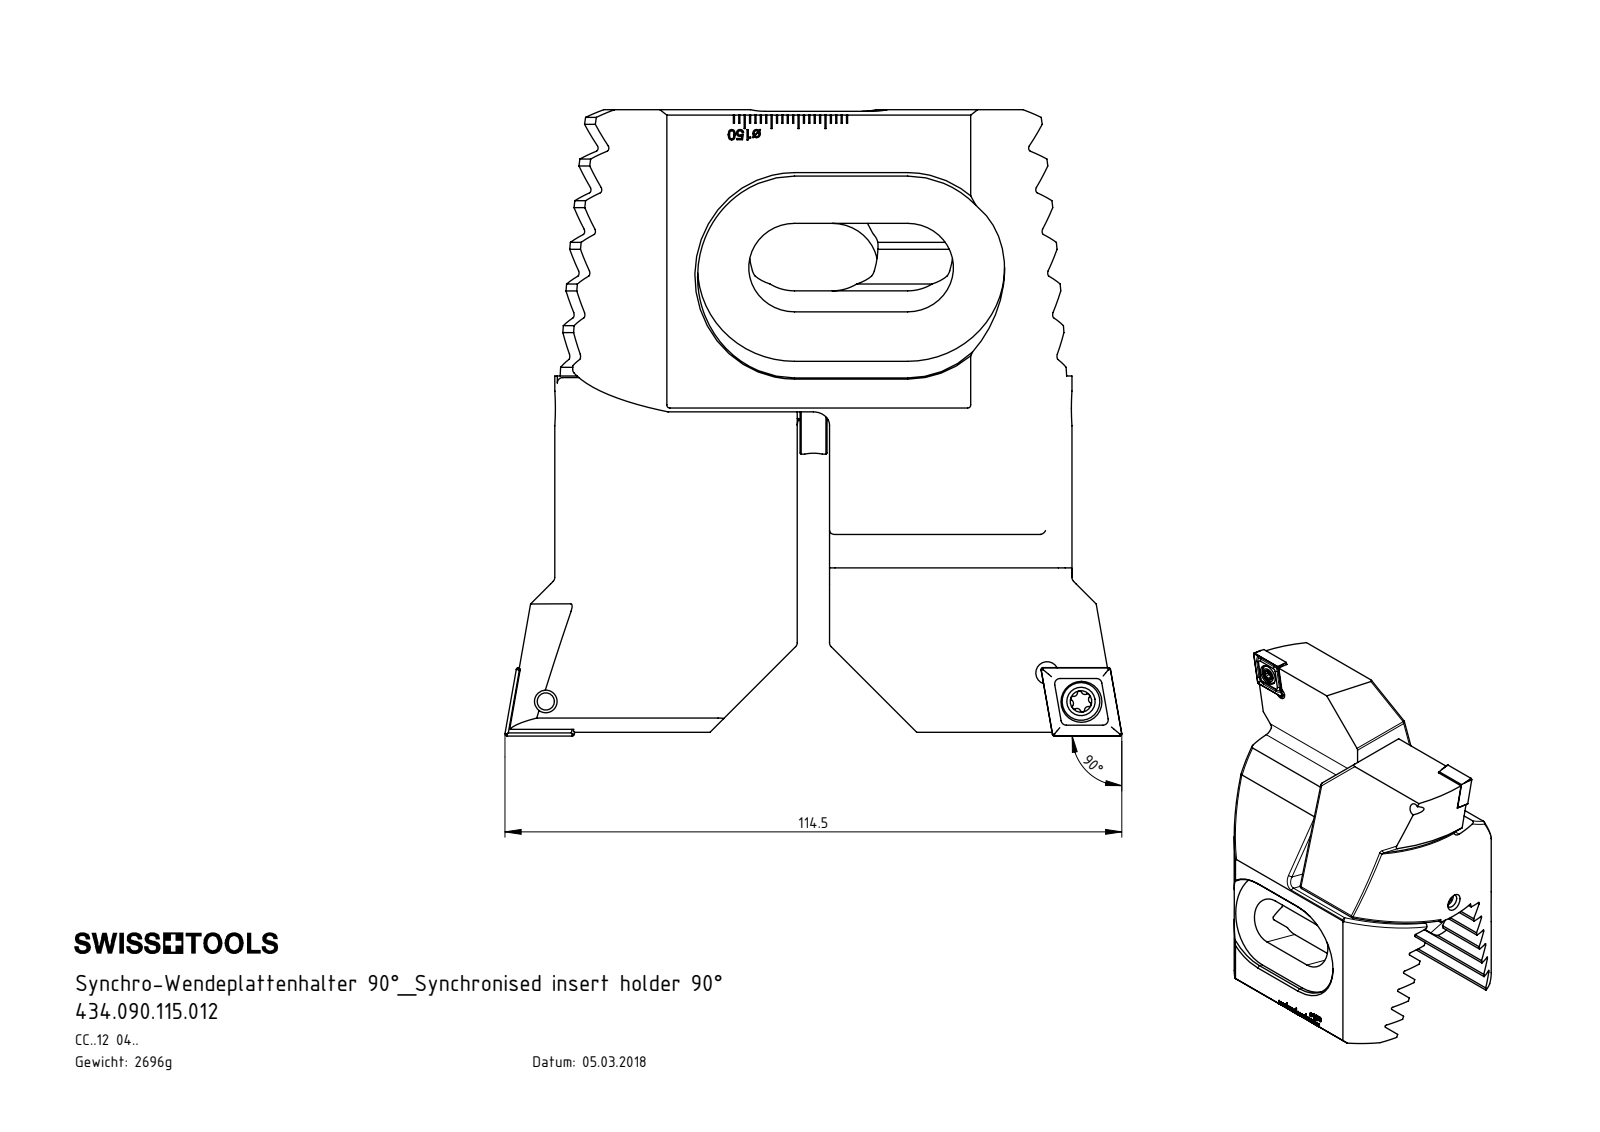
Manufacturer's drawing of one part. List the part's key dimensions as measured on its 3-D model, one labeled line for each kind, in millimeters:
Part name (STEP PRODUCT): Z42-ER3.002.005_A; ISO 4026 - M4 x 5; WCC-ER2.001.010_A; 434.090.115.012 (+4 more)
STEP written by: SolidWorks 2017 (CONFIG_CONTROL_DESIGN)
Units: millimetres
Bodies: 11 solids, 853 faces (469 planar, 154 cylindrical, 230 other)
Overall size (bounding box): 115.5 × 114.5 × 75.2
Volume: 343 499 mm³ · Surface area: 65 522 mm²
Round holes (diameter × count): ⌀4.2 ×4, ⌀3.3 ×3, ⌀2 ×2, ⌀5.5 ×2, ⌀7.6 ×2, ⌀5 ×1
Round bosses / shafts (diameter × count): ⌀4 ×3, ⌀7 ×2, ⌀5 ×2, ⌀17 ×1, ⌀6 ×1, ⌀3.8 ×1
Partial cylindrical surfaces — rounded edges, fillets, slot ends (radius × count): R1 ×16, R0.39 ×12, R0.58 ×12, R0.69 ×8, R3 ×6, R0.69 ×4, R8.5 ×4, R12 ×4
Main face-to-face distances: 6.93, 20.78, 27.71, 13.85, 13.86, 13.19, 37.3, 37.9, 6.92, 1.59
Hole centre spacings: 8.21, 8.33, 25, 93.2, 93.29, 99.43, 48.3, 86.76
